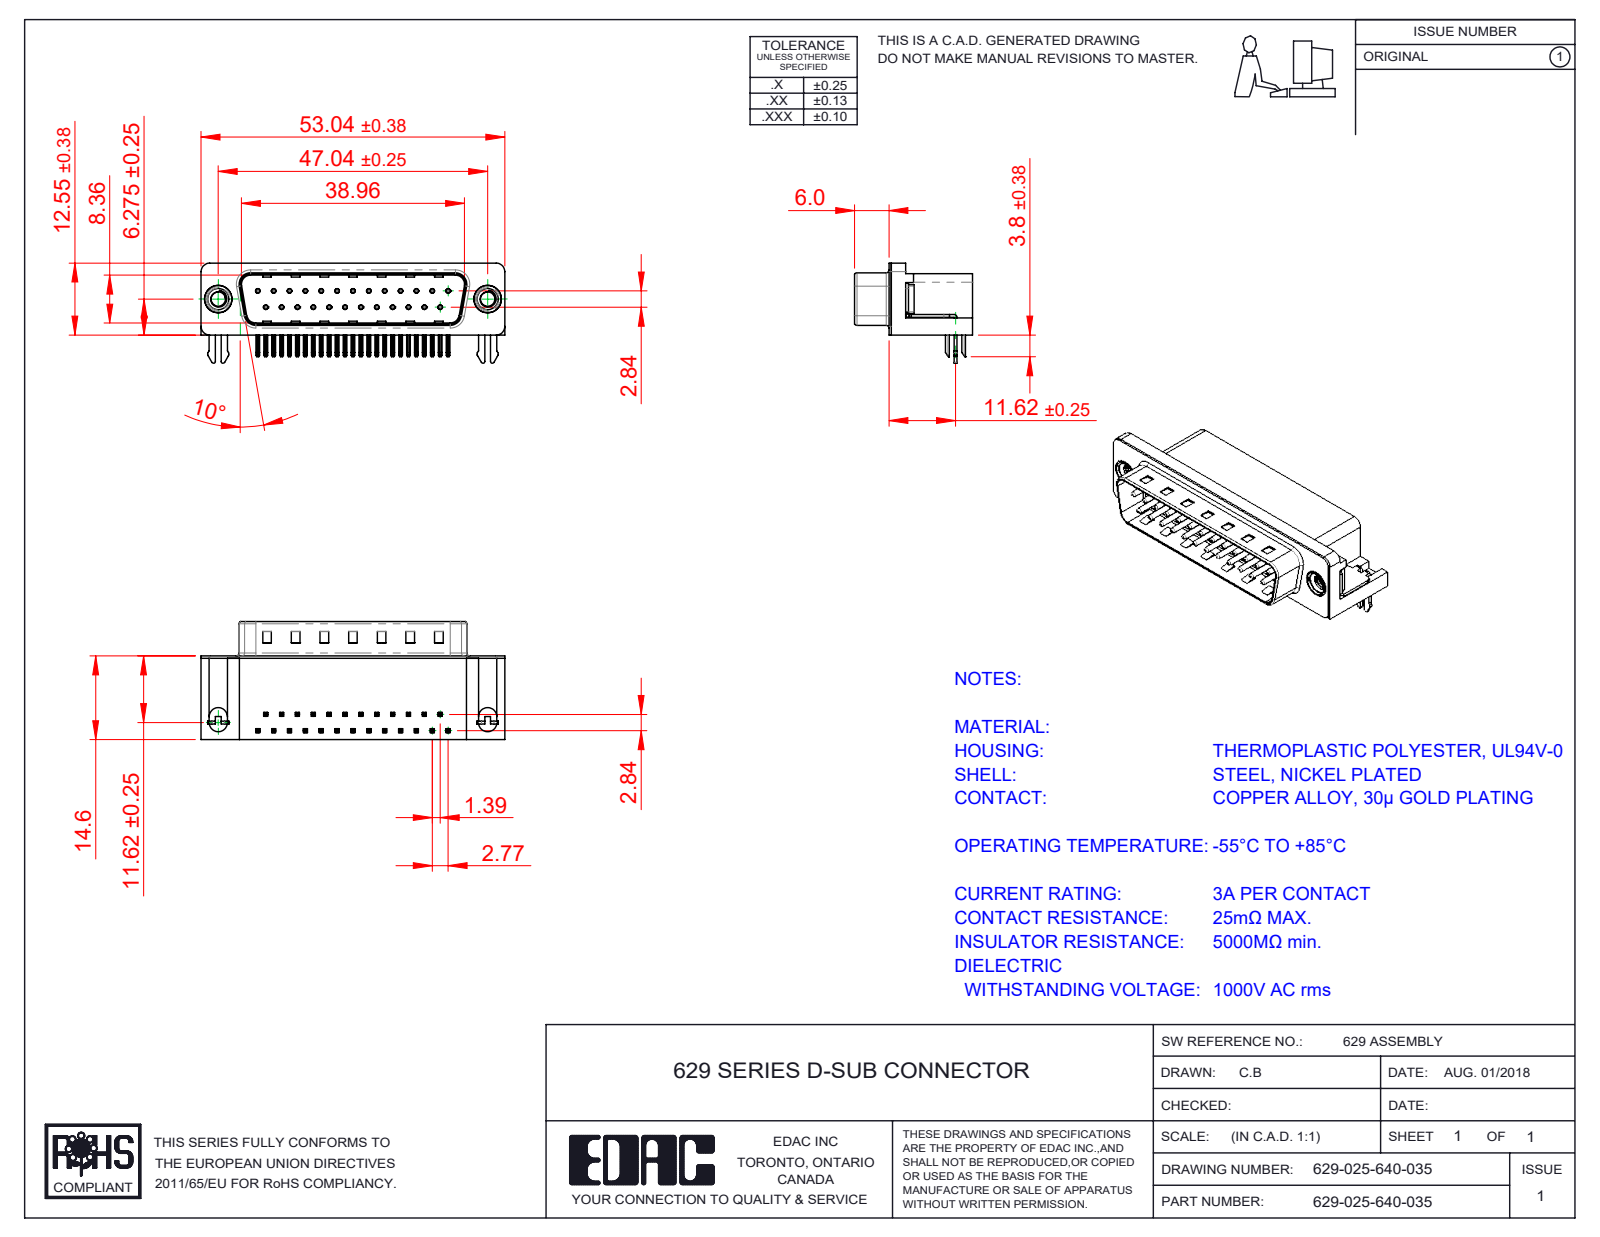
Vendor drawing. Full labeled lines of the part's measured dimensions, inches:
Part name (STEP PRODUCT): 629 M3 Threaded Rivet; 629 Shell_25 Socket; 629 Contact Bottom; 629 Contact Top (+3 more)
STEP written by: SolidWorks 2020 (CONFIG_CONTROL_DESIGN)
Units: inches
Bodies: 31 solids, 2301 faces (1435 planar, 671 cylindrical, 195 other)
Overall size (bounding box): 2.088 × 0.811 × 0.688
Volume: 0.447 in³ · Surface area: 12.8 in²
Round holes (diameter × count): ⌀0.014 ×25, ⌀0.031 ×25, ⌀0.098 ×2, ⌀0.157 ×2, ⌀0.189 ×2, ⌀0.197 ×2
Round bosses / shafts (diameter × count): ⌀0.03 ×25, ⌀0.193 ×2, ⌀0.187 ×2, ⌀0.154 ×2
Partial cylindrical surfaces — rounded edges, fillets, slot ends (radius × count): R0.01 ×108, R0.005 ×50, R0.039 ×16, R0.02 ×14, R0.063 ×8, R0.059 ×7, R0.013 ×4, R0.035 ×4
Main face-to-face distances: 0.016, 0.408, 0.559, 0.083, 0.345, 0.067, 0.412, 0.428, 0.575, 0.461
Hole centre spacings: 0.124, 0.109, 0.218, 0.327, 0.436, 0.545, 0.654, 0.198
